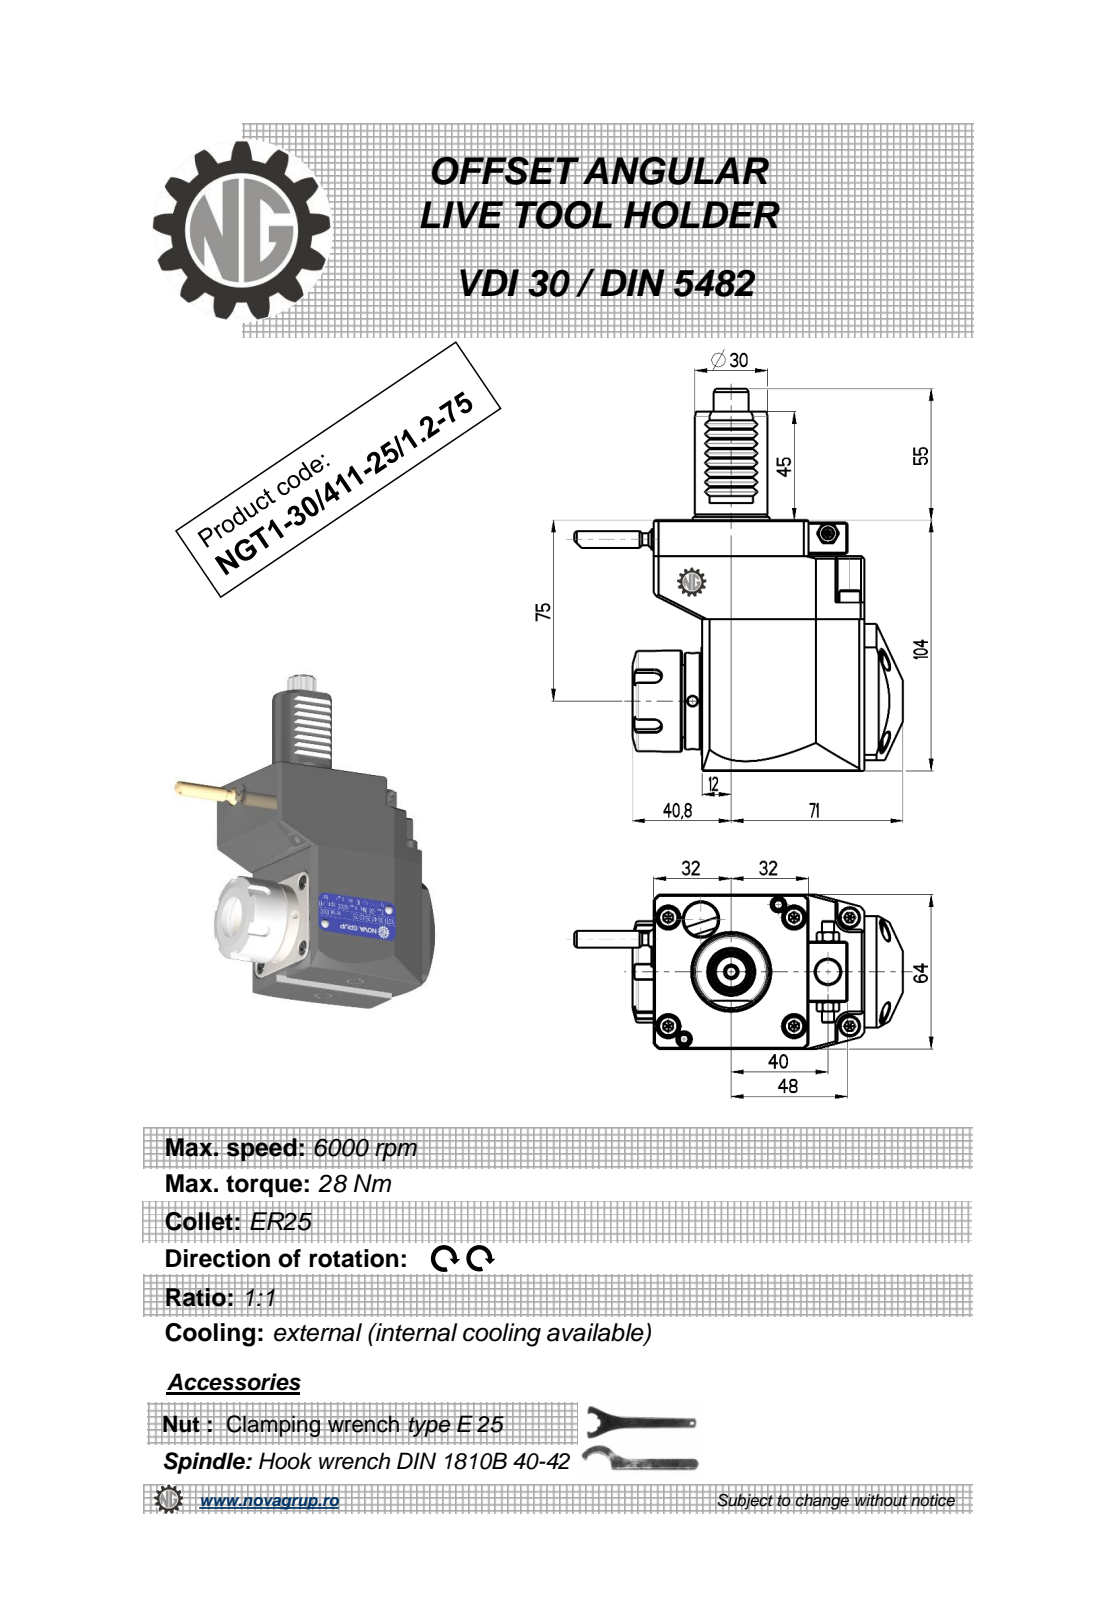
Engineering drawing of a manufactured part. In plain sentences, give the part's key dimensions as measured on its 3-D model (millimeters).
The part is named "NGT1_30_411_25_1_2_75". Its 3-D file was written by "PRO/ENGINEER BY PARAMETRIC TECHNOLOGY CORPORATION, 2010280 (CONFIG_CONTROL_DESIGN)". It is 1 solid with 469 faces: 194 planar, 118 cylindrical and 157 other. Overall it measures 159 by 135.88 by 65.4 millimeters. Its volume is 553 568 cubic millimeters and its surface area 53 064 square millimeters. Round holes: 2 of diameter 4, 2 of diameter 4.2, 1 of diameter 2.5, 1 of diameter 3, 1 of diameter 9.5, 1 of diameter 10, 1 of diameter 20.3. Round bosses or shafts: 2 of diameter 8.96, 2 of diameter 5, 1 of diameter 42, 1 of diameter 40, 1 of diameter 33, 1 of diameter 30, 1 of diameter 7. Partial cylindrical surfaces (rounded edges, fillets, slot ends): 16 of radius 2.81, 12 of radius 0.26, 8 of radius 0.3, 5 of radius 3, 4 of radius 3.5, 1 of radius 5.67, 1 of radius 7.25, 1 of radius 32. The main face-to-face distances are 64, 104, 87, 67.2, 19.8, 20, 15, 89, 67, 7. The hole center spacings are 13.54, 15.95, 40, 55.95, 68, 68.35, 89.22.
